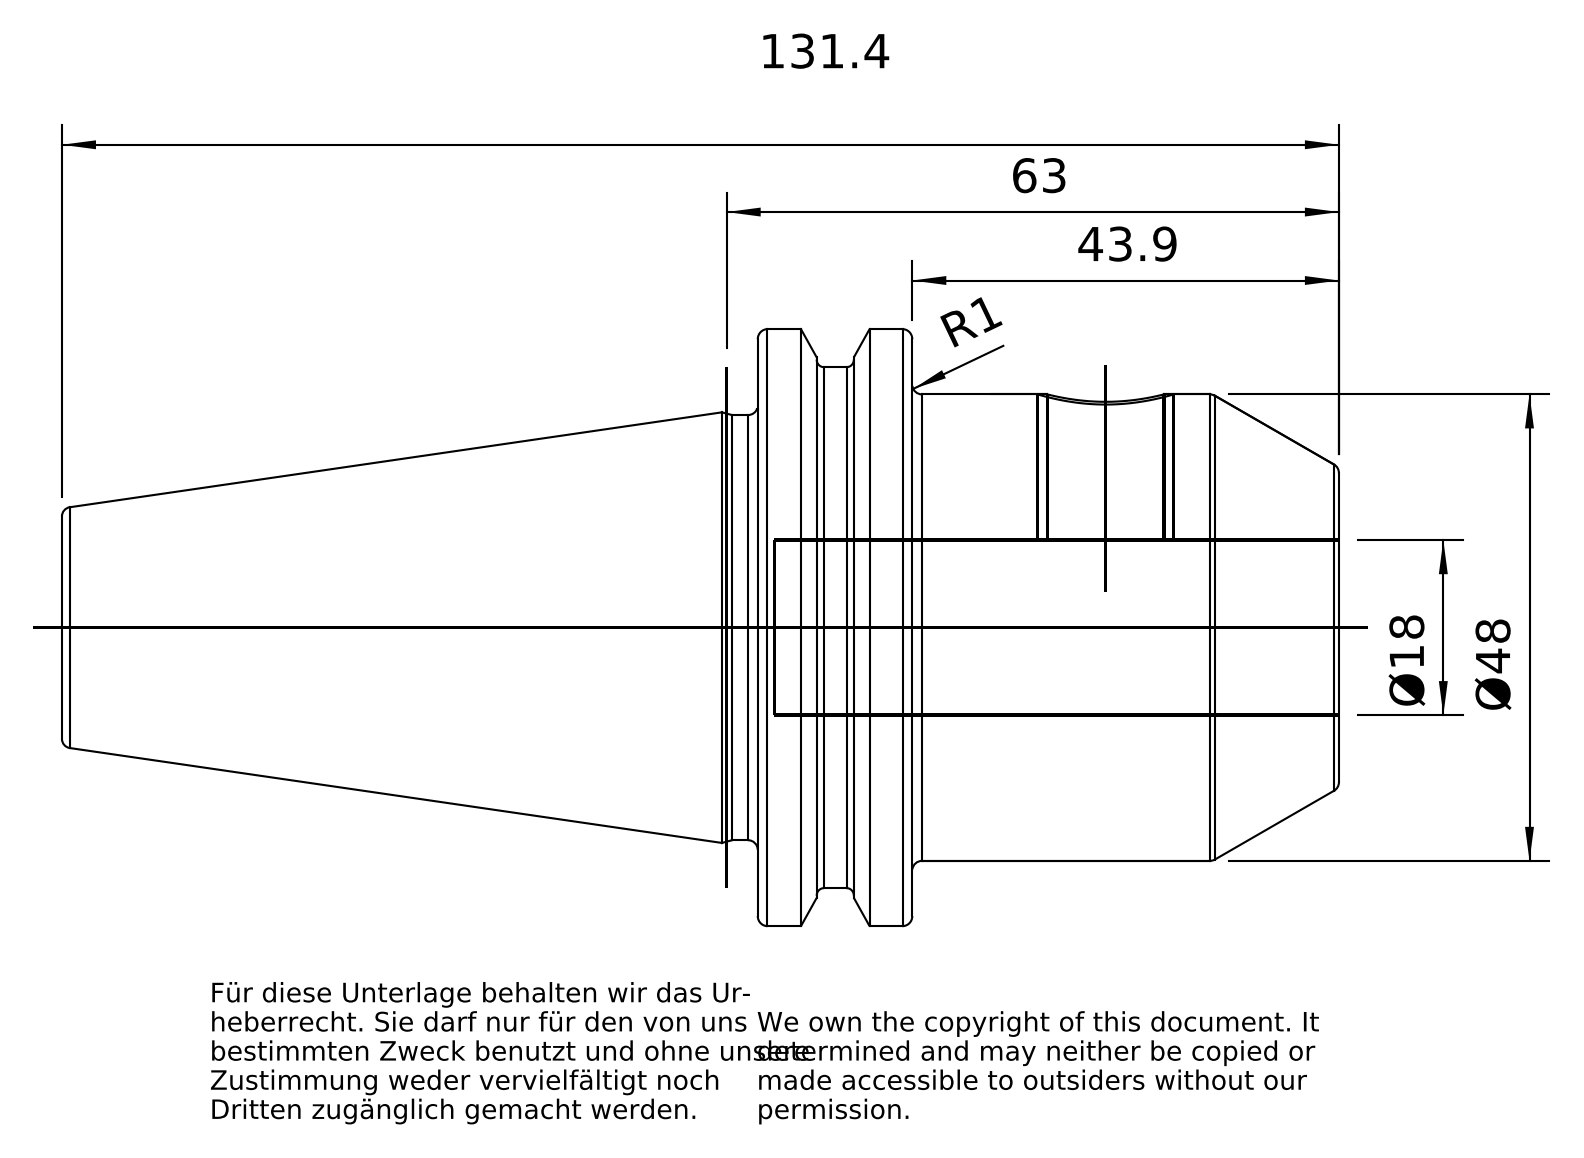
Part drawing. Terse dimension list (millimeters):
name: 40-300-18
written by: PRO/ENGINEER BY PARAMETRIC TECHNOLOGY CORPORATION, 2010430 (CONFIG_CONTROL_DESIGN)
unit: mm
bodies: 1 solid, 100 faces (23 planar, 28 cylindrical, 49 other)
size: 131.25 × 63.52 × 61.42
volume: 162 168 mm³; area: 29 900 mm²
holes: 1× ⌀12, 1× ⌀13.84, 1× ⌀14, 1× ⌀17.01, 1× ⌀17.5, 1× ⌀18
bosses: 1× ⌀48, 1× ⌀43.75, 1× ⌀16.01
rounds: 1× R1.35, 1× R28, 1× R31.76
face distances: 15.85, 59.8, 43.95, 47.4, 1.7, 14.15, 58.1, 16.2, 71.45, 73.15
